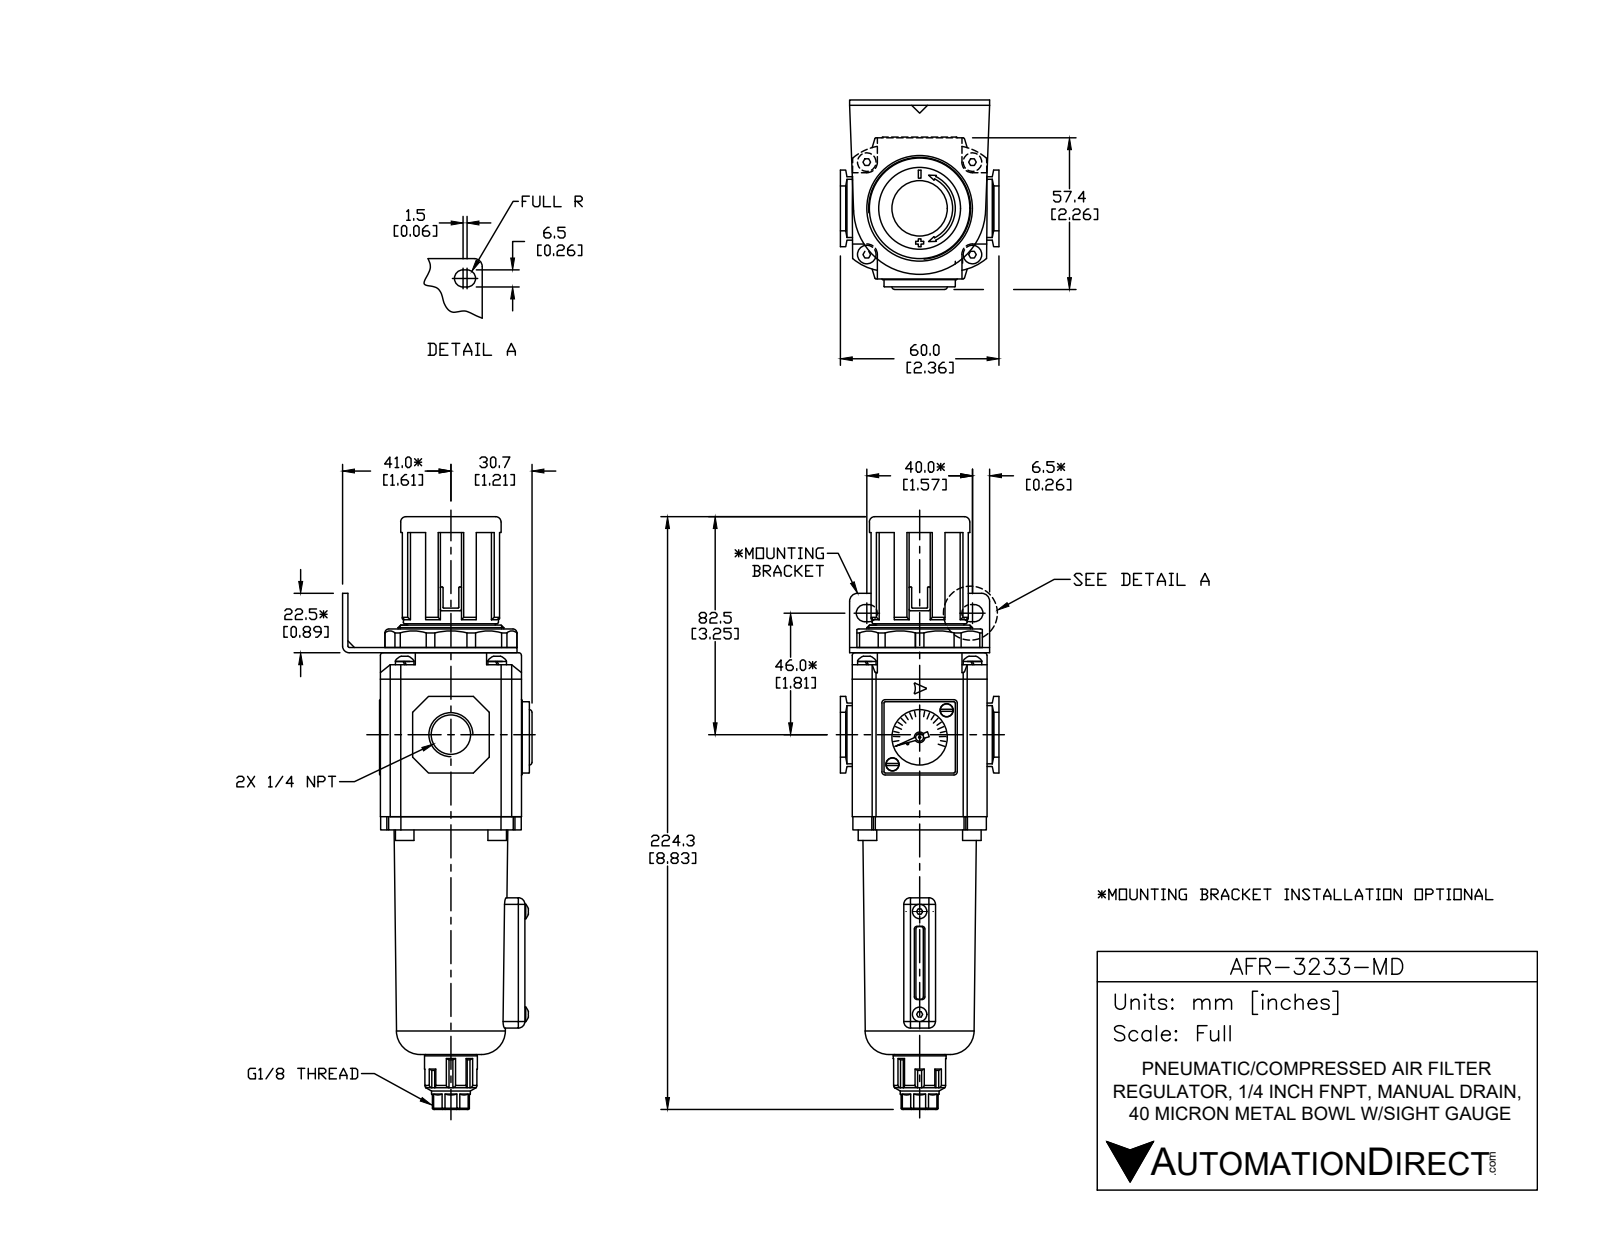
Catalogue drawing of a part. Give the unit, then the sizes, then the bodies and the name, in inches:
Units: inches
Overall size (bounding box): 8.831 × 2.835 × 2.362
Round holes (diameter × count): ⌀0.118 ×6, ⌀0.079 ×1, ⌀0.244 ×1, ⌀0.562 ×1, ⌀0.827 ×1, ⌀1.181 ×1, ⌀1.26 ×1
Round bosses / shafts (diameter × count): ⌀0.217 ×6, ⌀0.276 ×4, ⌀0.106 ×2, ⌀1.575 ×1, ⌀1.496 ×1, ⌀1.417 ×1, ⌀1.319 ×1, ⌀0.806 ×1
Partial cylindrical surfaces — rounded edges, fillets, slot ends (radius × count): R0.039 ×16, R0.047 ×10, R0.051 ×8, R0.098 ×8, R0.374 ×8, R0.783 ×8, R0.02 ×6, R0.128 ×6
Main face-to-face distances: 0.079, 2.441, 2.52, 2.102, 2.008, 0.039, 2.185, 2.063, 2.638, 0.177
Hole centre spacings: 1.046, 0.571, 1.378, 1.575, 2.093, 1.141
Volume: 21.91 in³ · Surface area: 100.4 in²
Bodies: 16 solids, 686 faces (418 planar, 181 cylindrical, 87 other)
Part name (STEP PRODUCT): AFR-3333-MD
STEP written by: SolidWorks 2015 (CONFIG_CONTROL_DESIGN)
